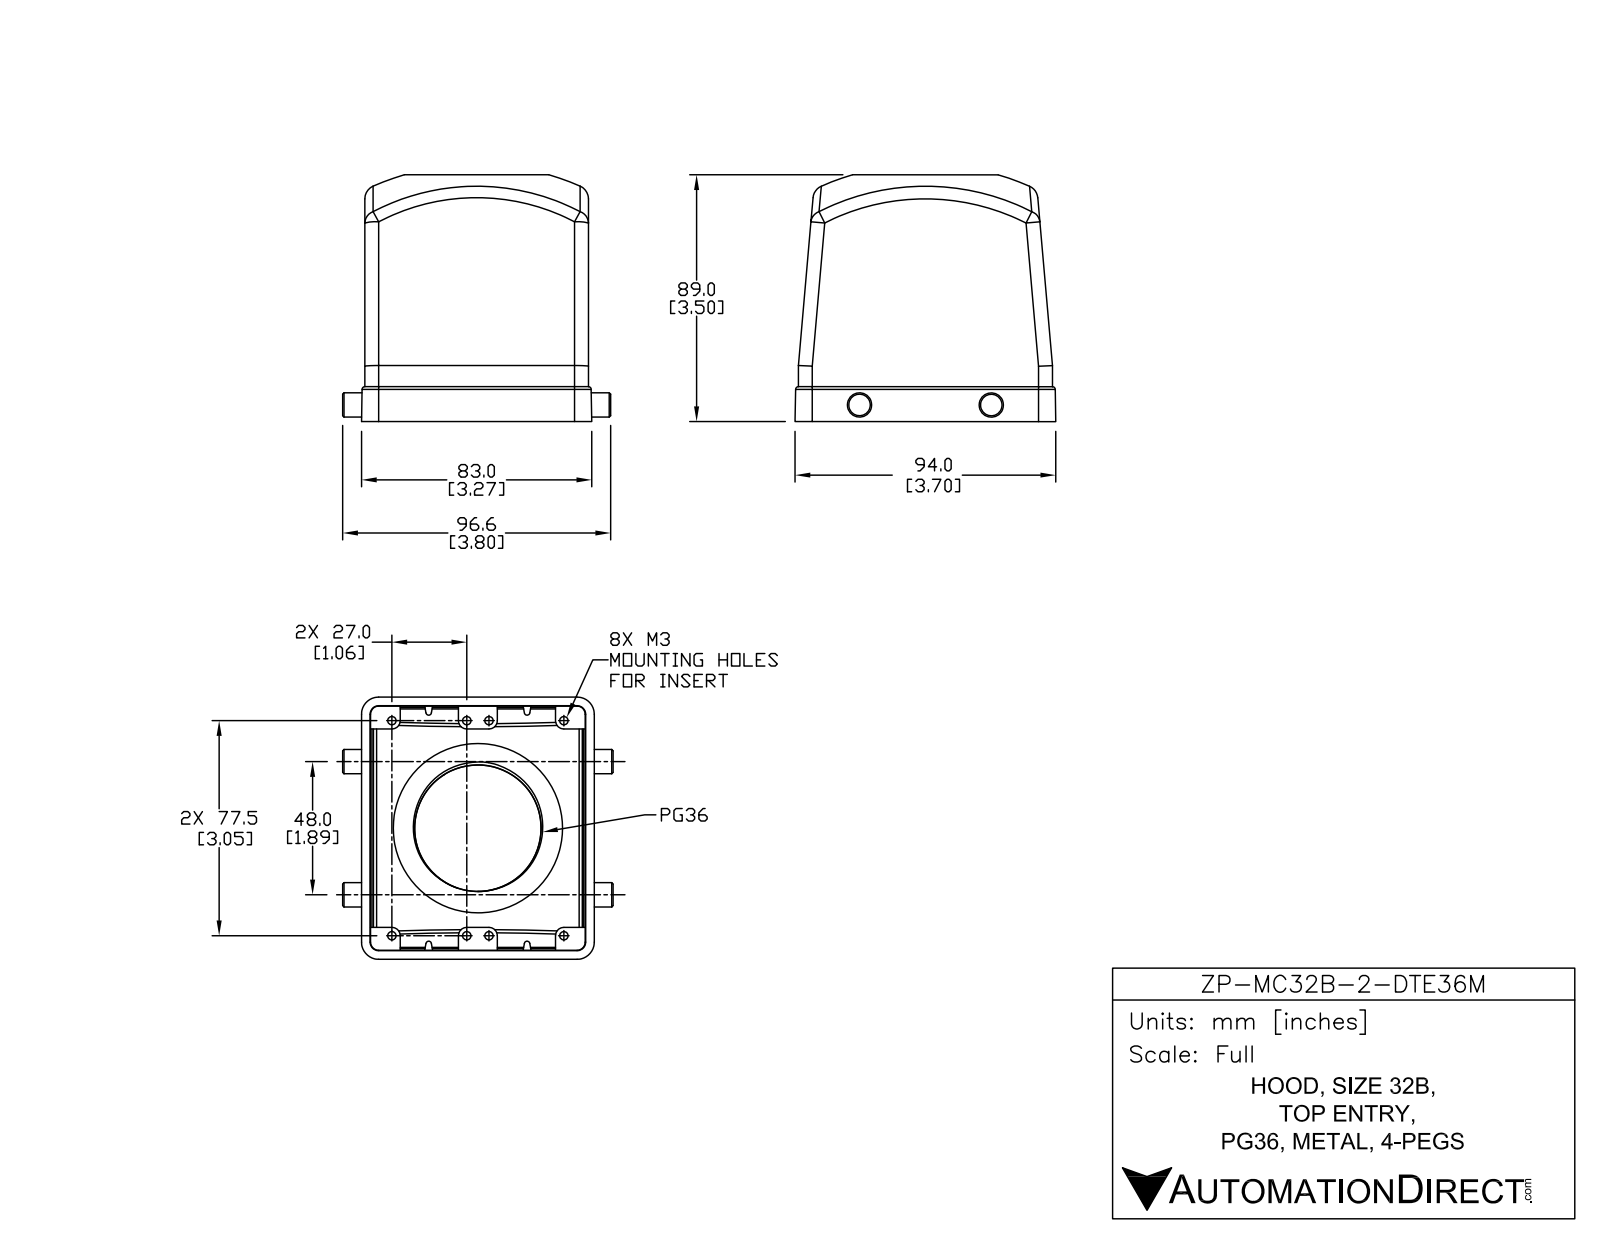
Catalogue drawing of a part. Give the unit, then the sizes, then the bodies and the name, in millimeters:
Units: millimetres
Overall size (bounding box): 97.5 × 94.5 × 89
Round holes (diameter × count): ⌀3 ×8, ⌀2.55 ×2, ⌀45.6 ×1, ⌀53 ×1
Round bosses / shafts (diameter × count): ⌀8.75 ×2, ⌀61 ×1
Partial cylindrical surfaces — rounded edges, fillets, slot ends (radius × count): R1 ×8, R3 ×8, R5 ×8, R0.5 ×4
Main face-to-face distances: 3.1, 78.4, 81.5, 75.3, 3.09, 10.3, 81.8, 71.5, 81.9, 89
Hole centre spacings: 27, 35, 38.96, 49.62, 77.5, 82.07, 85.04, 8
Volume: 123 625 mm³ · Surface area: 67 978 mm²
Bodies: 1 solid, 208 faces (90 planar, 77 cylindrical, 41 other)
Part name (STEP PRODUCT): ZP-MC32B-2-DTE36M
STEP written by: SolidWorks 2014 (AUTOMOTIVE_DESIGN)
